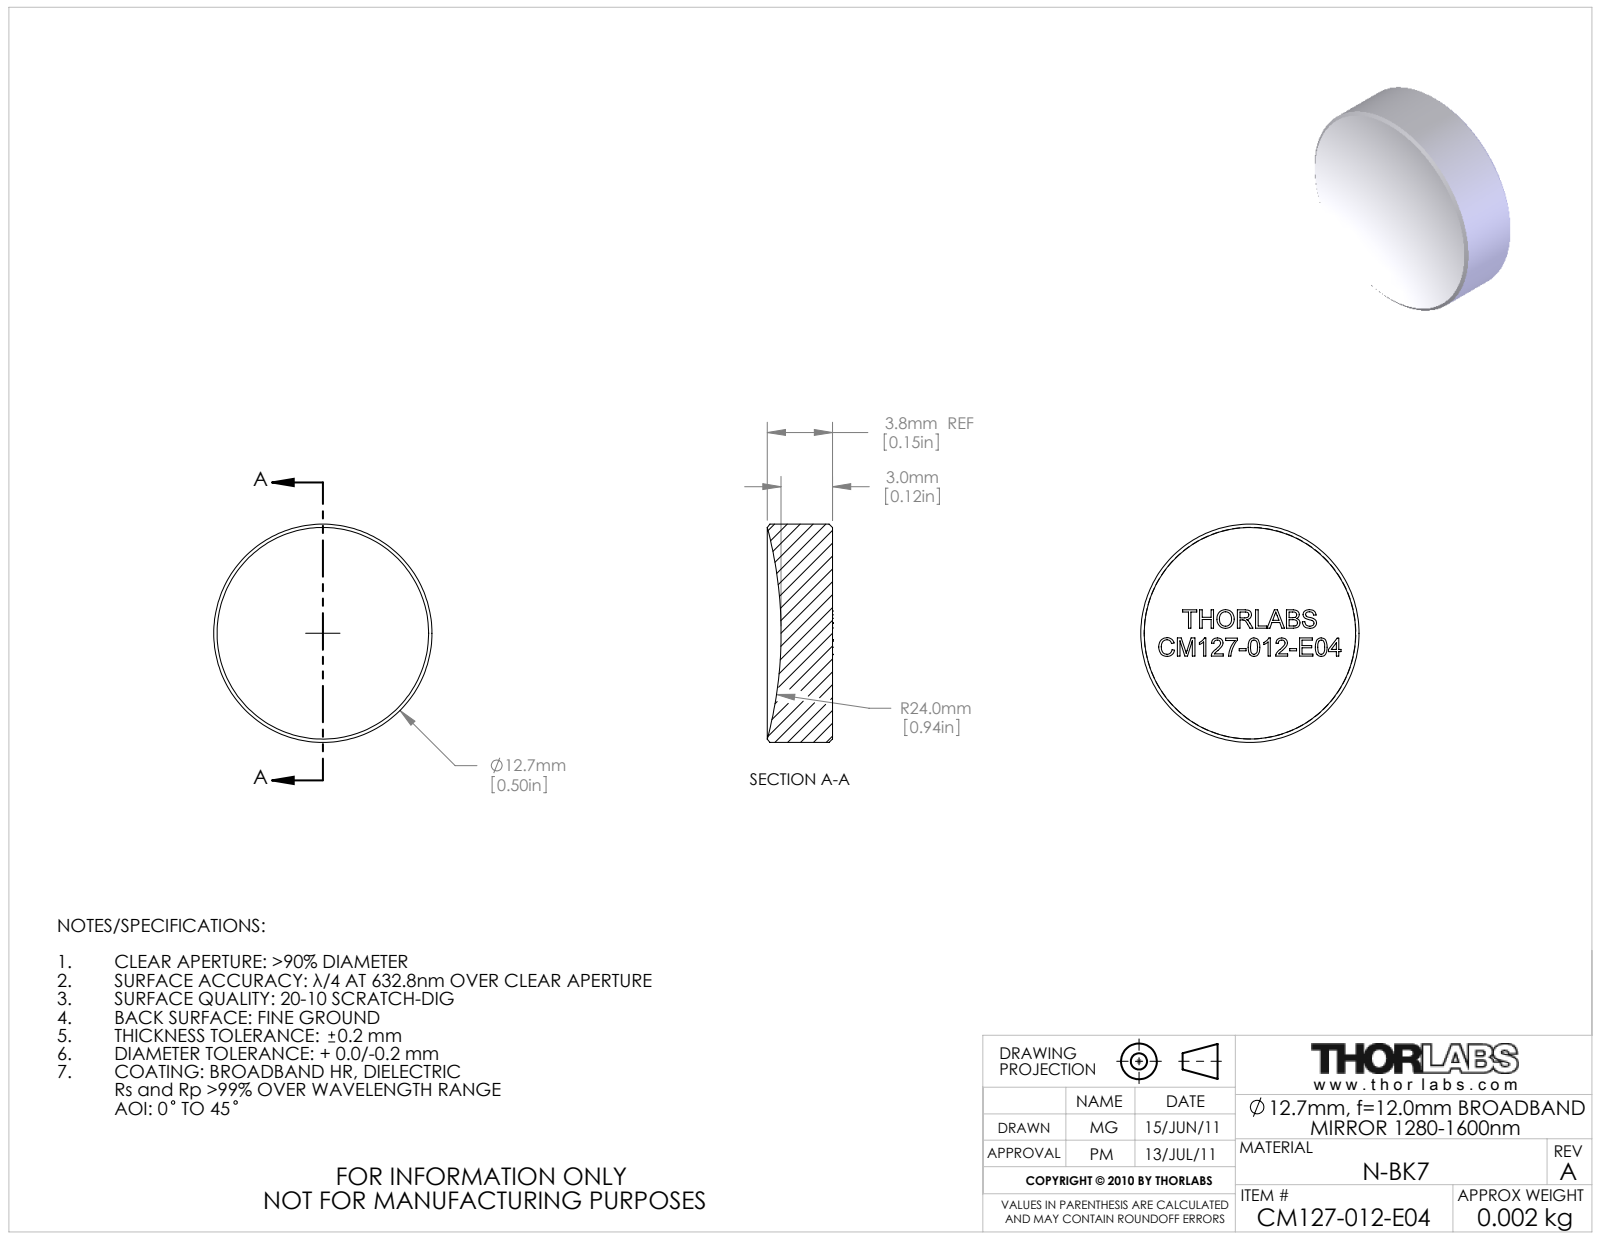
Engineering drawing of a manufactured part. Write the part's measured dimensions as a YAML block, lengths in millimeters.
part_name: "22653-E0W"
step_written_by: "SolidWorks 2011 (AUTOMOTIVE_DESIGN)"
units: millimeters
bodies: {solids: 0, faces: 44, planar: 34, cylindrical: 2, other: 8}
overall_size: [12.7, 12.7, 3.8]
round_bosses_or_shafts:
  - {diameter: 12.7, count: 1}
face_to_face_distances: [2.08, 1.02, 1.06]
